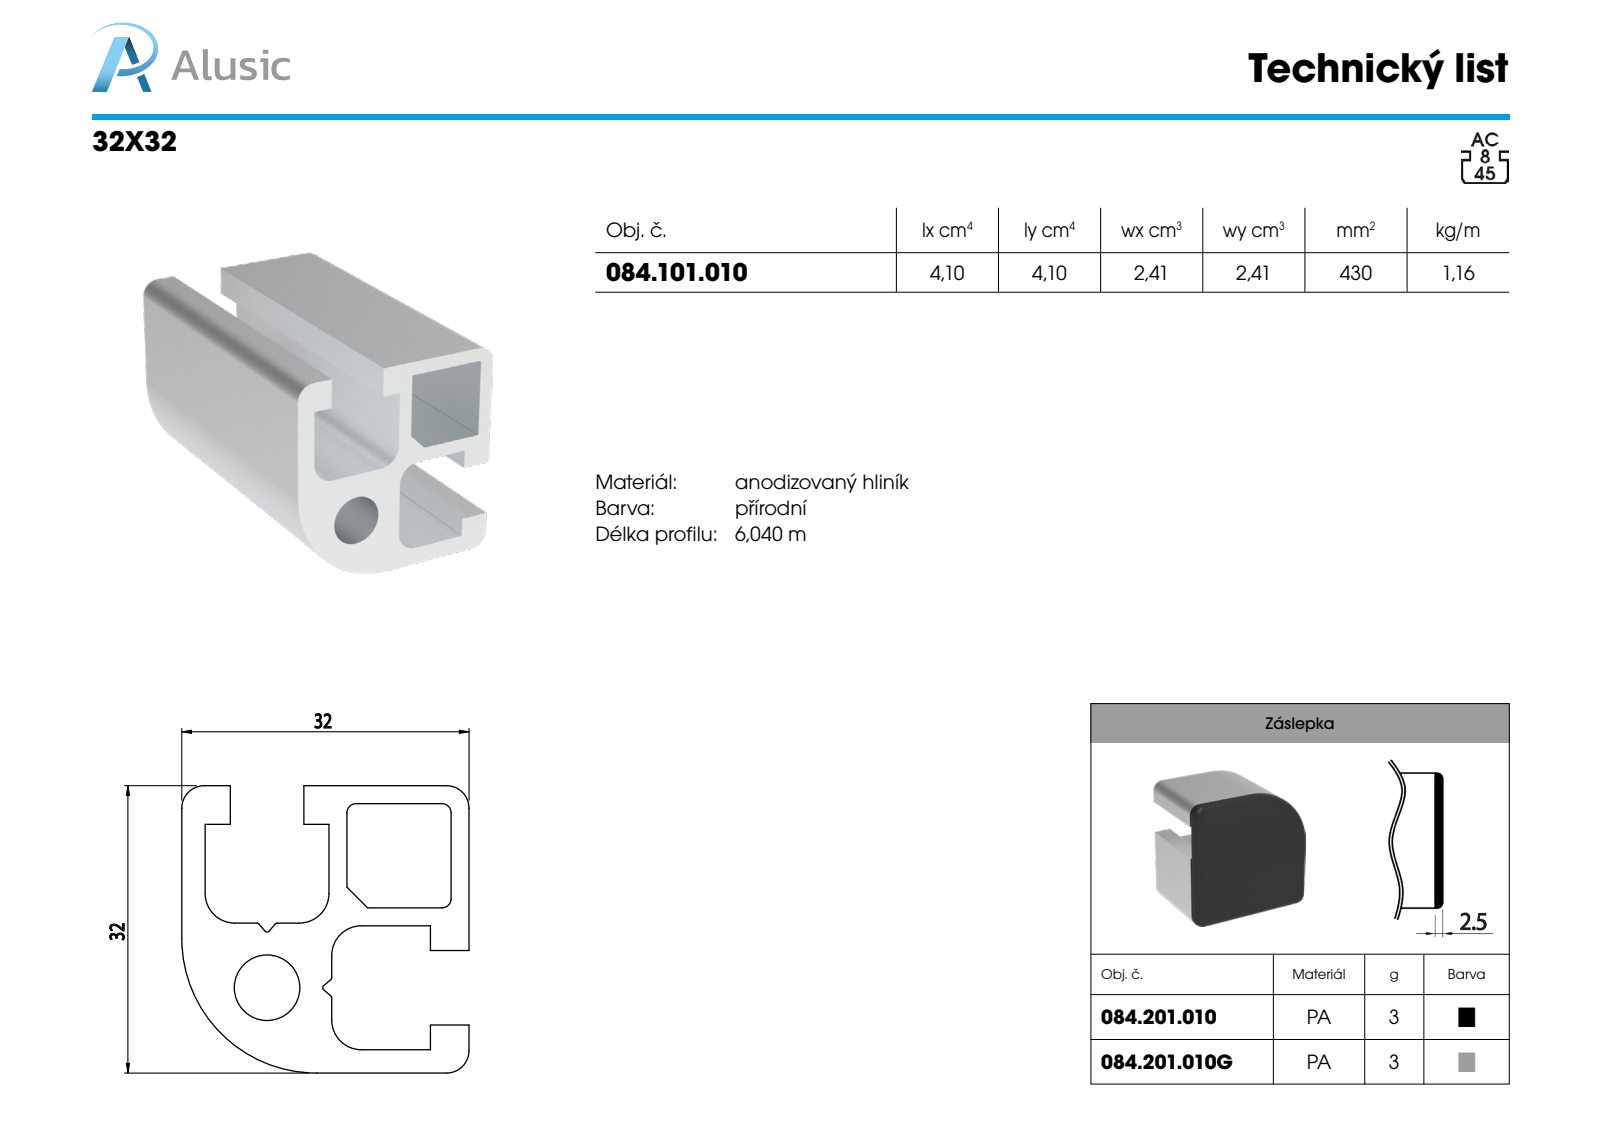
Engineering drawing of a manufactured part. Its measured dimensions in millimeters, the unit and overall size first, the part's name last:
Units: millimetres
Overall size (bounding box): 100 × 32 × 32
Round holes (diameter × count): ⌀7.3 ×1
Partial cylindrical surfaces — rounded edges, fillets, slot ends (radius × count): R3 ×4, R2.5 ×3, R15 ×1
Main face-to-face distances: 2, 13.6, 32, 30, 18.4, 11.6, 2.75, 11.05, 2.6, 15.8
Volume: 43 066 mm³ · Surface area: 27 299 mm²
Bodies: 1 solid, 37 faces (27 planar, 10 cylindrical, 0 other)
Part name (STEP PRODUCT): 084.101.010
STEP written by: SolidWorks 2018 (AUTOMOTIVE_DESIGN)
